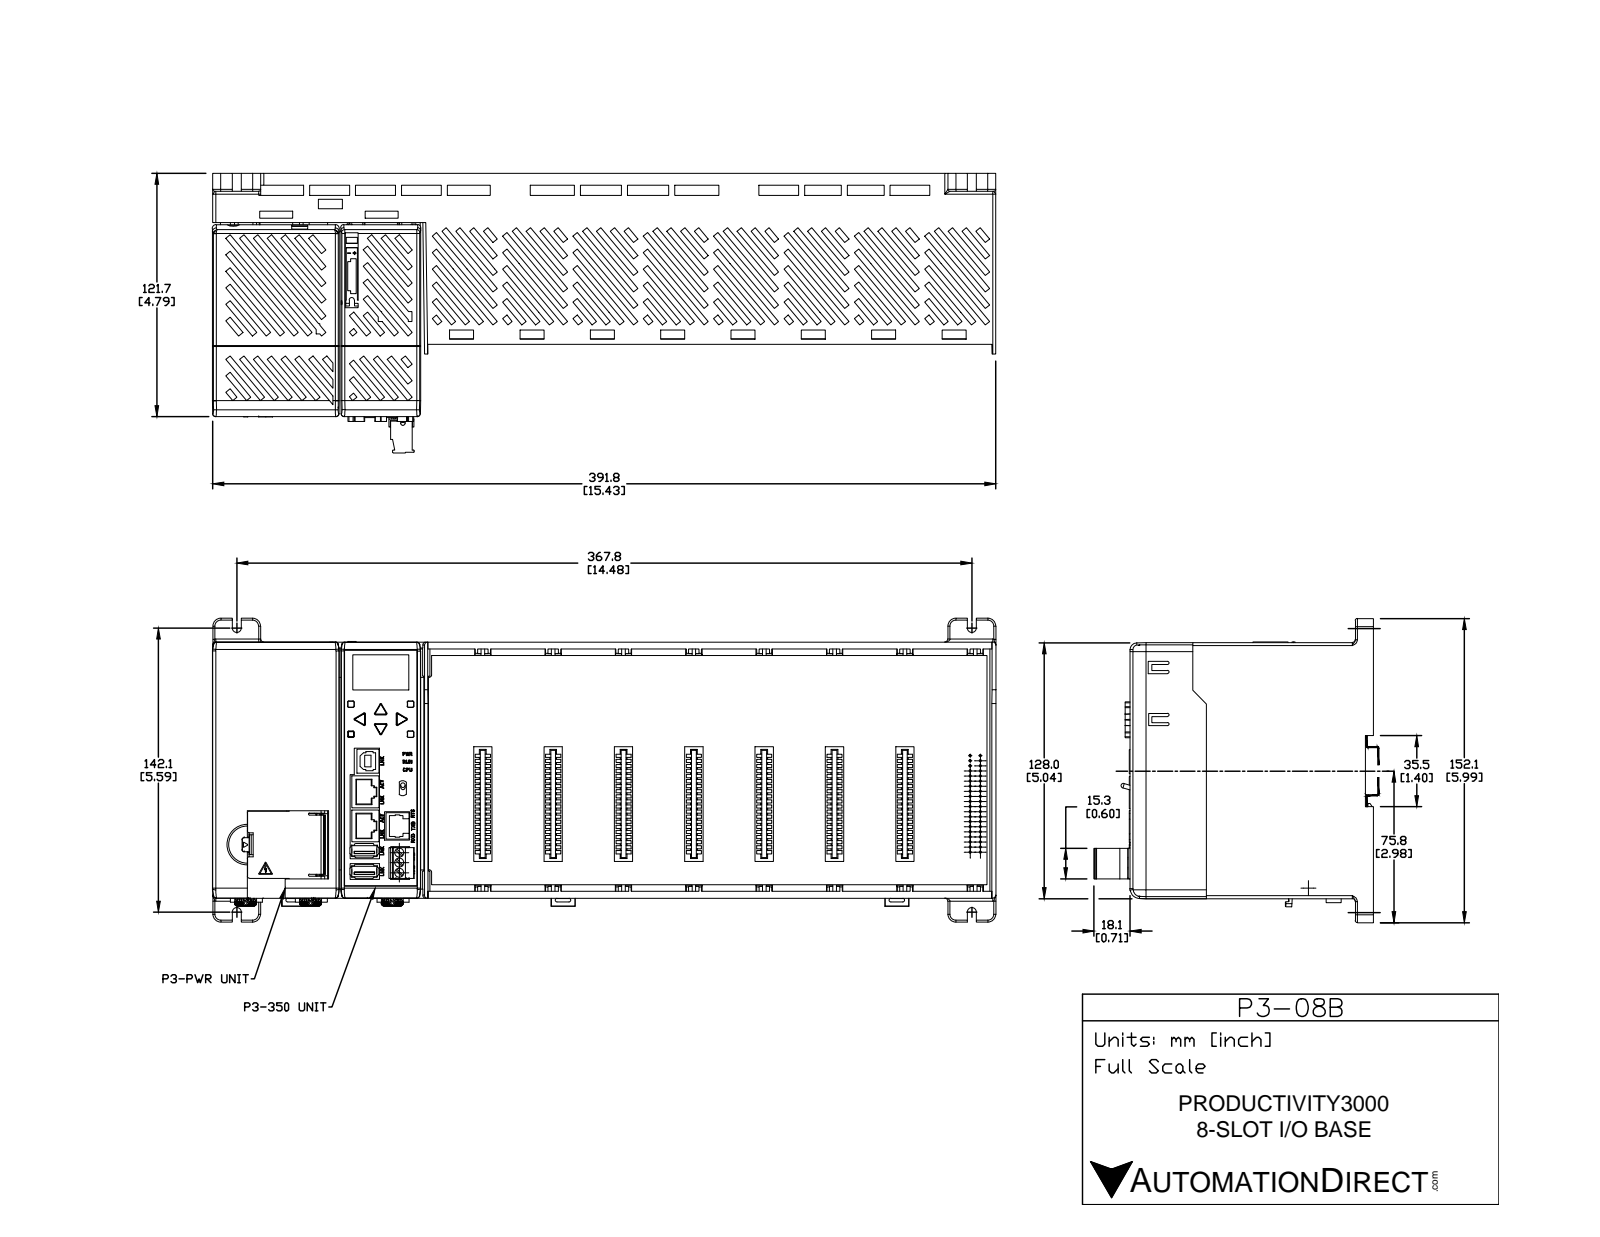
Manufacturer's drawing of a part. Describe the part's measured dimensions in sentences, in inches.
The part is named "P3-08B". Its 3-D file was written by "SolidWorks 2009 (CONFIG_CONTROL_DESIGN)". It is 1 solid with 511 faces: 499 planar, 12 cylindrical and 0 other. Overall it measures 15.43 by 5.98 by 3.5 inches. Its volume is 32.25 cubic inches and its surface area 597.3 square inches. Partial cylindrical surfaces (rounded edges, fillets, slot ends): 8 of radius 0.16, 4 of radius 0.09. The main face-to-face distances are 0.075, 0.429, 0.624, 0.549, 0.12, 0.504, 0.075, 5.04, 4.965, 4.89.
